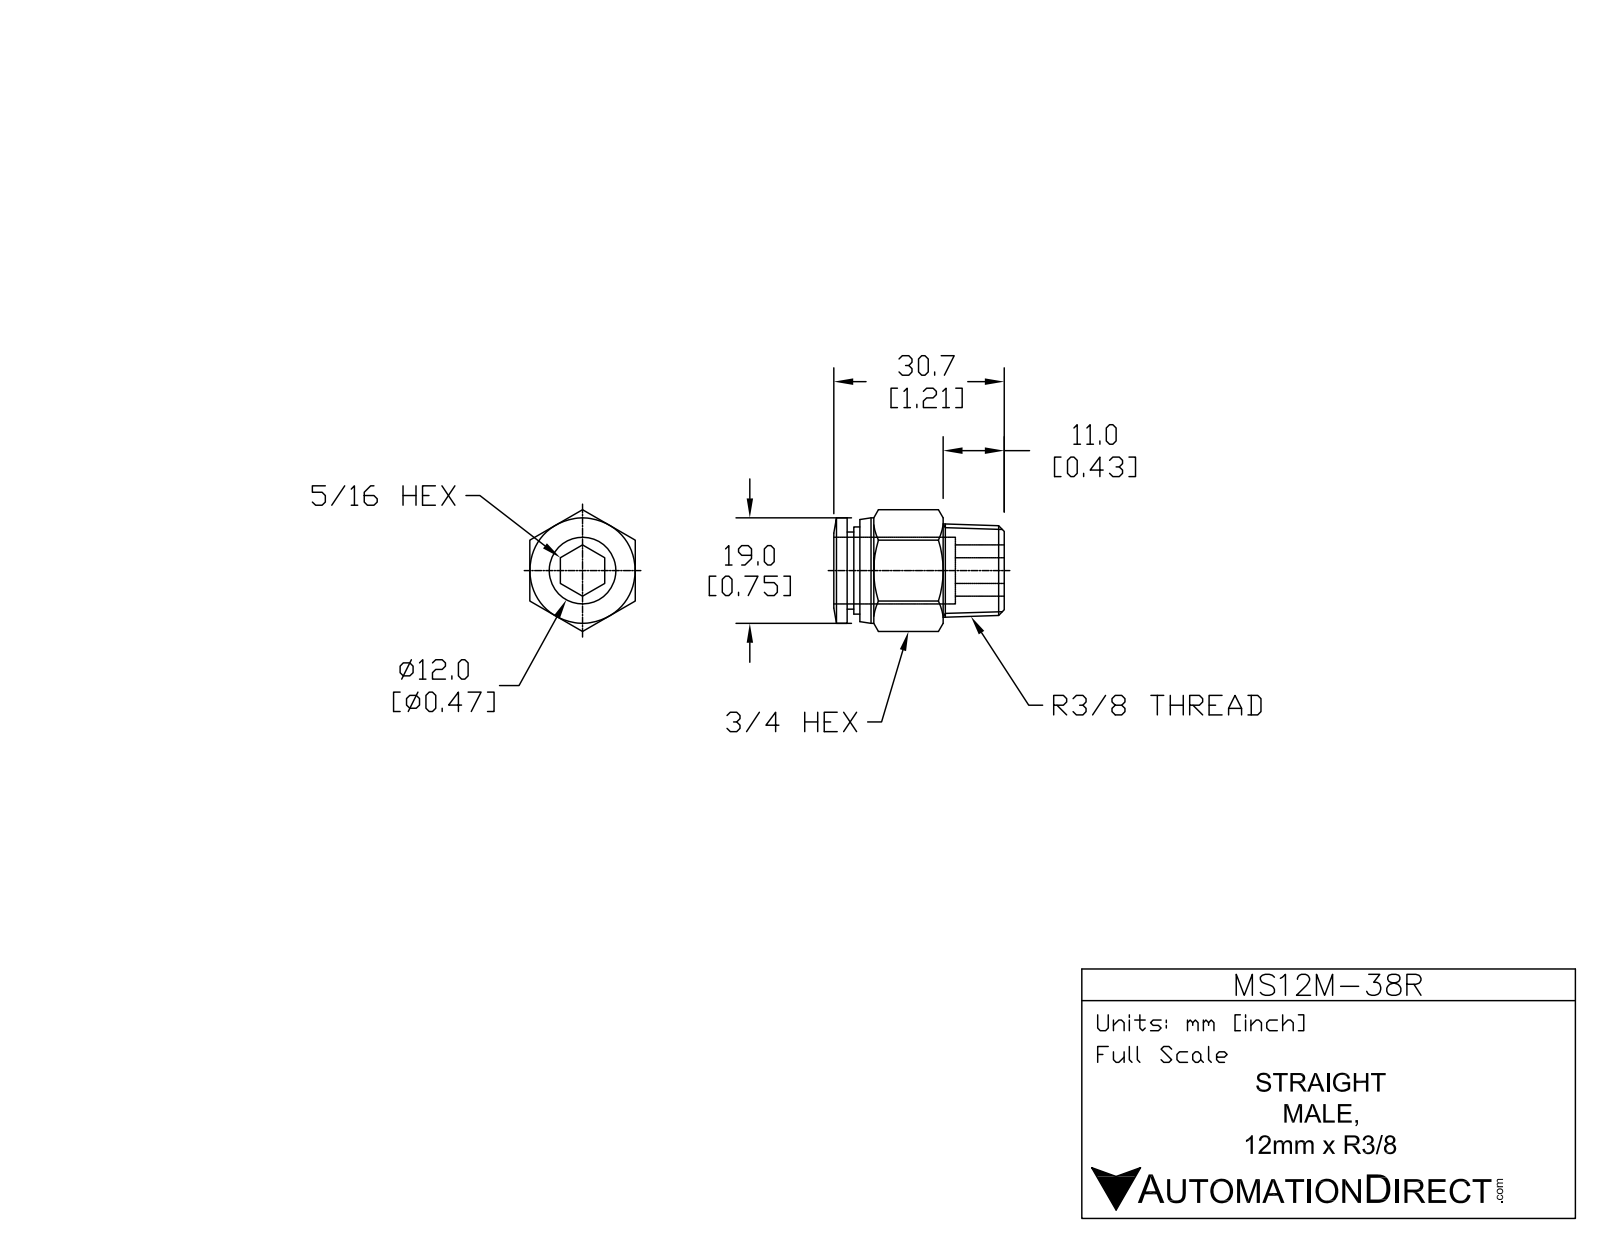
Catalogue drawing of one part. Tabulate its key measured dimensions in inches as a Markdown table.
| quantity | value |
| --- | --- |
| part name | MS12M-38R |
| STEP written by | SolidWorks 2015 (AUTOMOTIVE_DESIGN) |
| units | inches |
| bodies | 1 solid, 49 faces (13 planar, 12 cylindrical, 24 other) |
| overall size | 1.209 × 0.864 × 0.748 |
| volume | 0.283 in³ |
| surface area | 5.454 in² |
| round holes (diameter × count) | 0.394 × 1, 0.484 × 1 |
| round bosses / shafts (diameter × count) | 0.748 × 1, 0.618 × 1, 0.547 × 1 |
| main face-to-face distances | 0.748, 1.114, 1.024, 0.091, 0.433, 0.591, 0.681, 1.067, 0.634, 0.043 |
